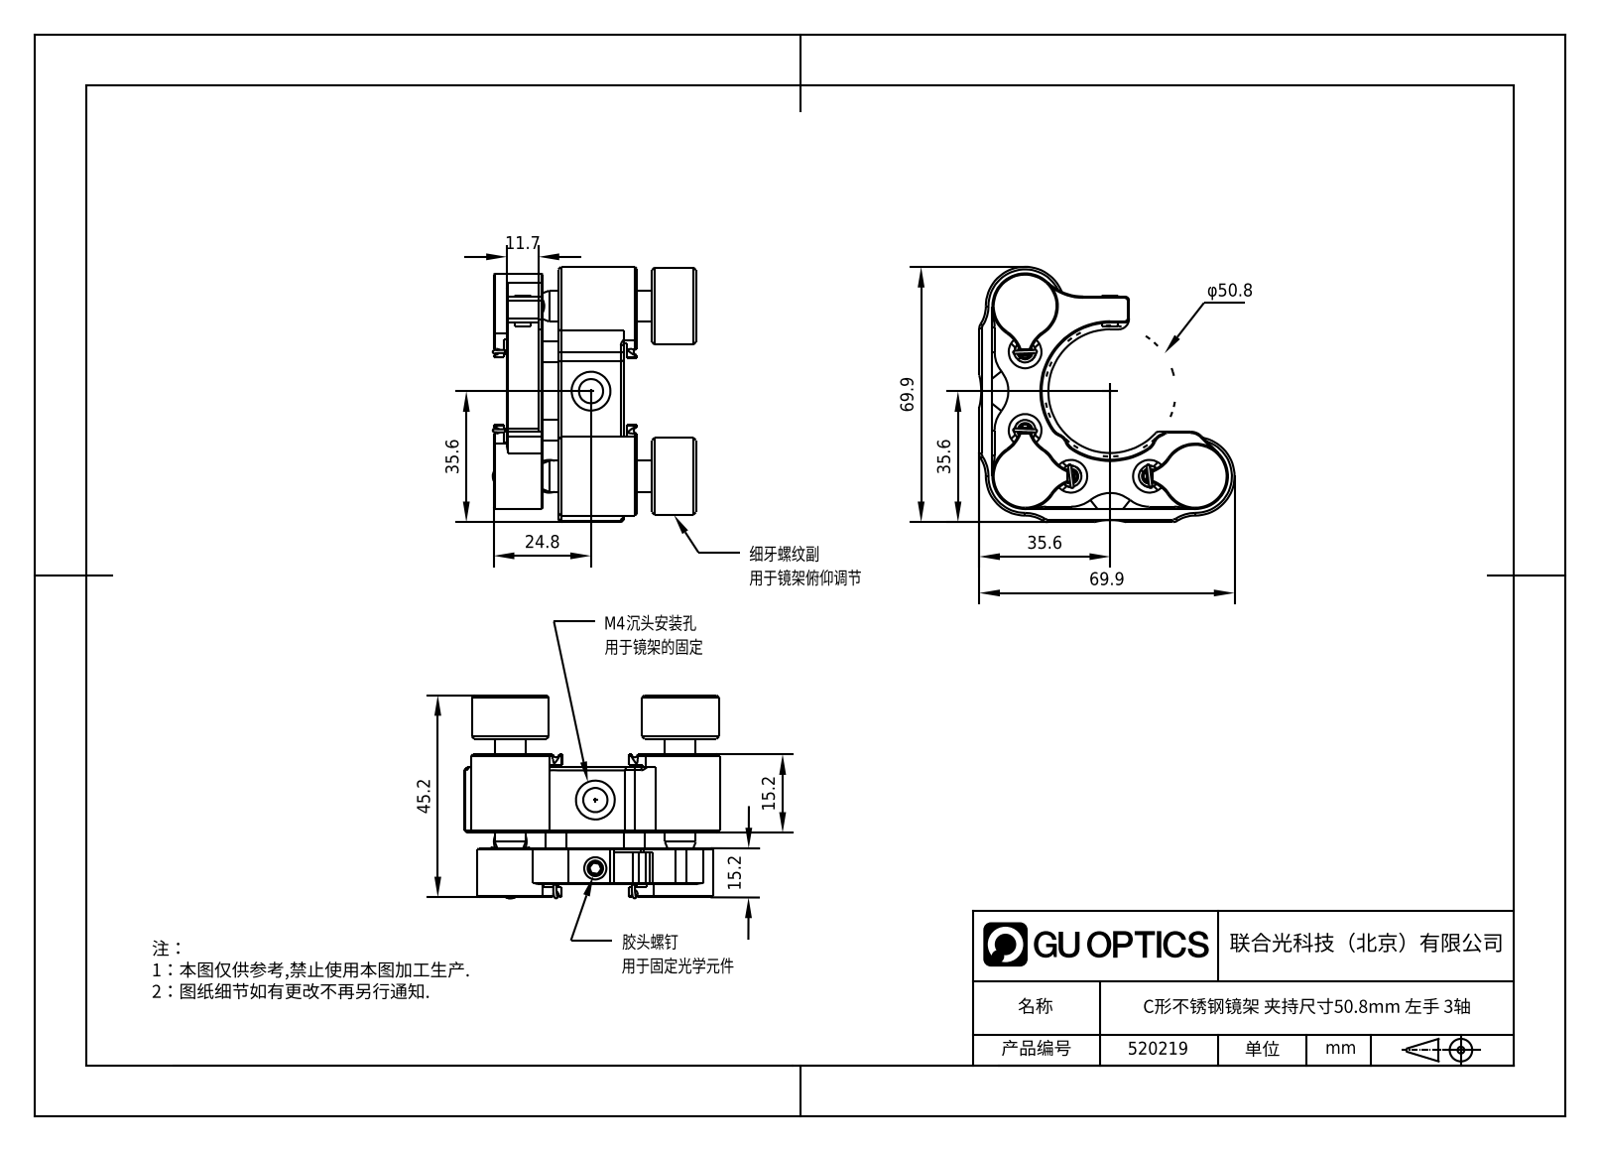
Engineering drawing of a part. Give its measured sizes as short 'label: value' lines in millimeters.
name: DXVS，真空型M6x0.25六角调节器，零部件，Rev.A_3.2.11.2.1-DXVS-0625-26.6; 1.1.19.28-ZJD-K2.0-3L; DXVS，真空M6x0.25细牙螺丝，Rev.A_3.2.11.2-DXVS-0625-26.6; 36.1，440c不锈钢滚珠_36.1.35_GZ-B6.35 (+3 more)
written by: SolidWorks 2021 (CONFIG_CONTROL_DESIGN)
unit: mm
bodies: 24 solids, 794 faces (217 planar, 205 cylindrical, 372 other)
size: 69.85 × 69.85 × 45.24
volume: 39 322 mm³; area: 24 213 mm²
holes: 7× ⌀6.35, 4× ⌀4.7, 4× ⌀7.54, 3× ⌀1.8, 3× ⌀3.99, 3× ⌀4, 3× ⌀6, 3× ⌀7, 2× ⌀2.01, 2× ⌀3.3
bosses: 8× ⌀4, 3× ⌀15, 3× ⌀5, 2× ⌀15.24, 2× ⌀3
rounds: 19× R6.48, 8× R3.17, 5× R3, 4× R1, 4× R4, 4× R64.14, 3× R0.6, 3× R6.35
face distances: 12.7, 15.87, 2.54, 3.17, 15.24, 18.41, 31.11, 28.57, 11.59, 14.13
hole spacings: 9.44, 43.9, 5, 9.5, 14.5, 34.46, 44.9, 53.34
